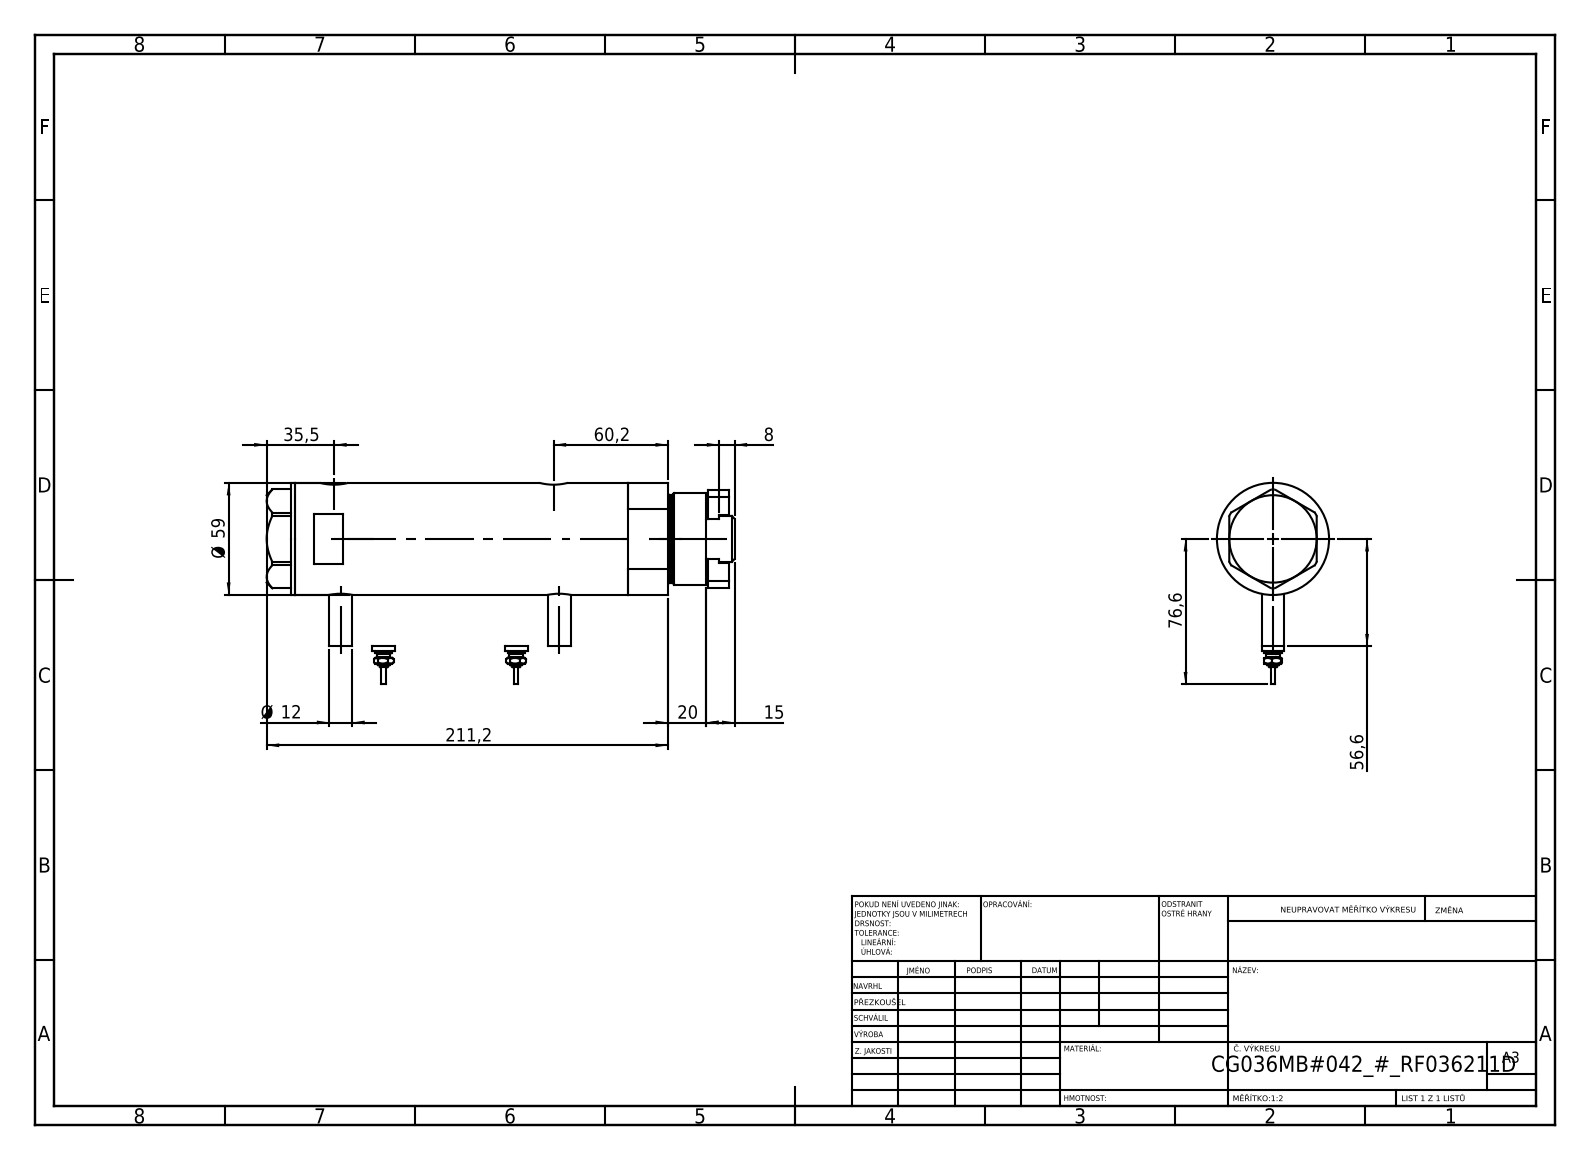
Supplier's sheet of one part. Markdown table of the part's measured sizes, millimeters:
| quantity | value |
| --- | --- |
| part name | Switch; V270CG_FRONT; V270CG_BACK; V270CG_VC (+2 more) |
| STEP written by | SolidWorks 2019 (CONFIG_CONTROL_DESIGN) |
| units | millimeters |
| bodies | 8 solids, 252 faces (103 planar, 85 cylindrical, 64 other) |
| overall size | 246.2 × 106.1 × 59 |
| volume | 589 628 mm³ |
| surface area | 121 616 mm² |
| round holes (diameter × count) | 6.1 × 4, 10.5 × 4, 9.73 × 2, 12.5 × 2, 15 × 2, 8.5 × 1, 25 × 1, 26.5 × 1, 36 × 1, 40 × 1, 52 × 1 |
| round bosses / shafts (diameter × count) | 12 × 4, 9 × 2, 7 × 2, 4.5 × 2, 2.5 × 2, 59 × 1, 48 × 1, 46 × 1 |
| main face-to-face distances | 137.2, 23.5, 113.7, 15, 2, 38.5, 152.2, 38, 231.2, 216.2 |
| hole center spacings | 19.92, 12, 37.98, 39.83, 2.9, 3.5, 112, 114.9 |
